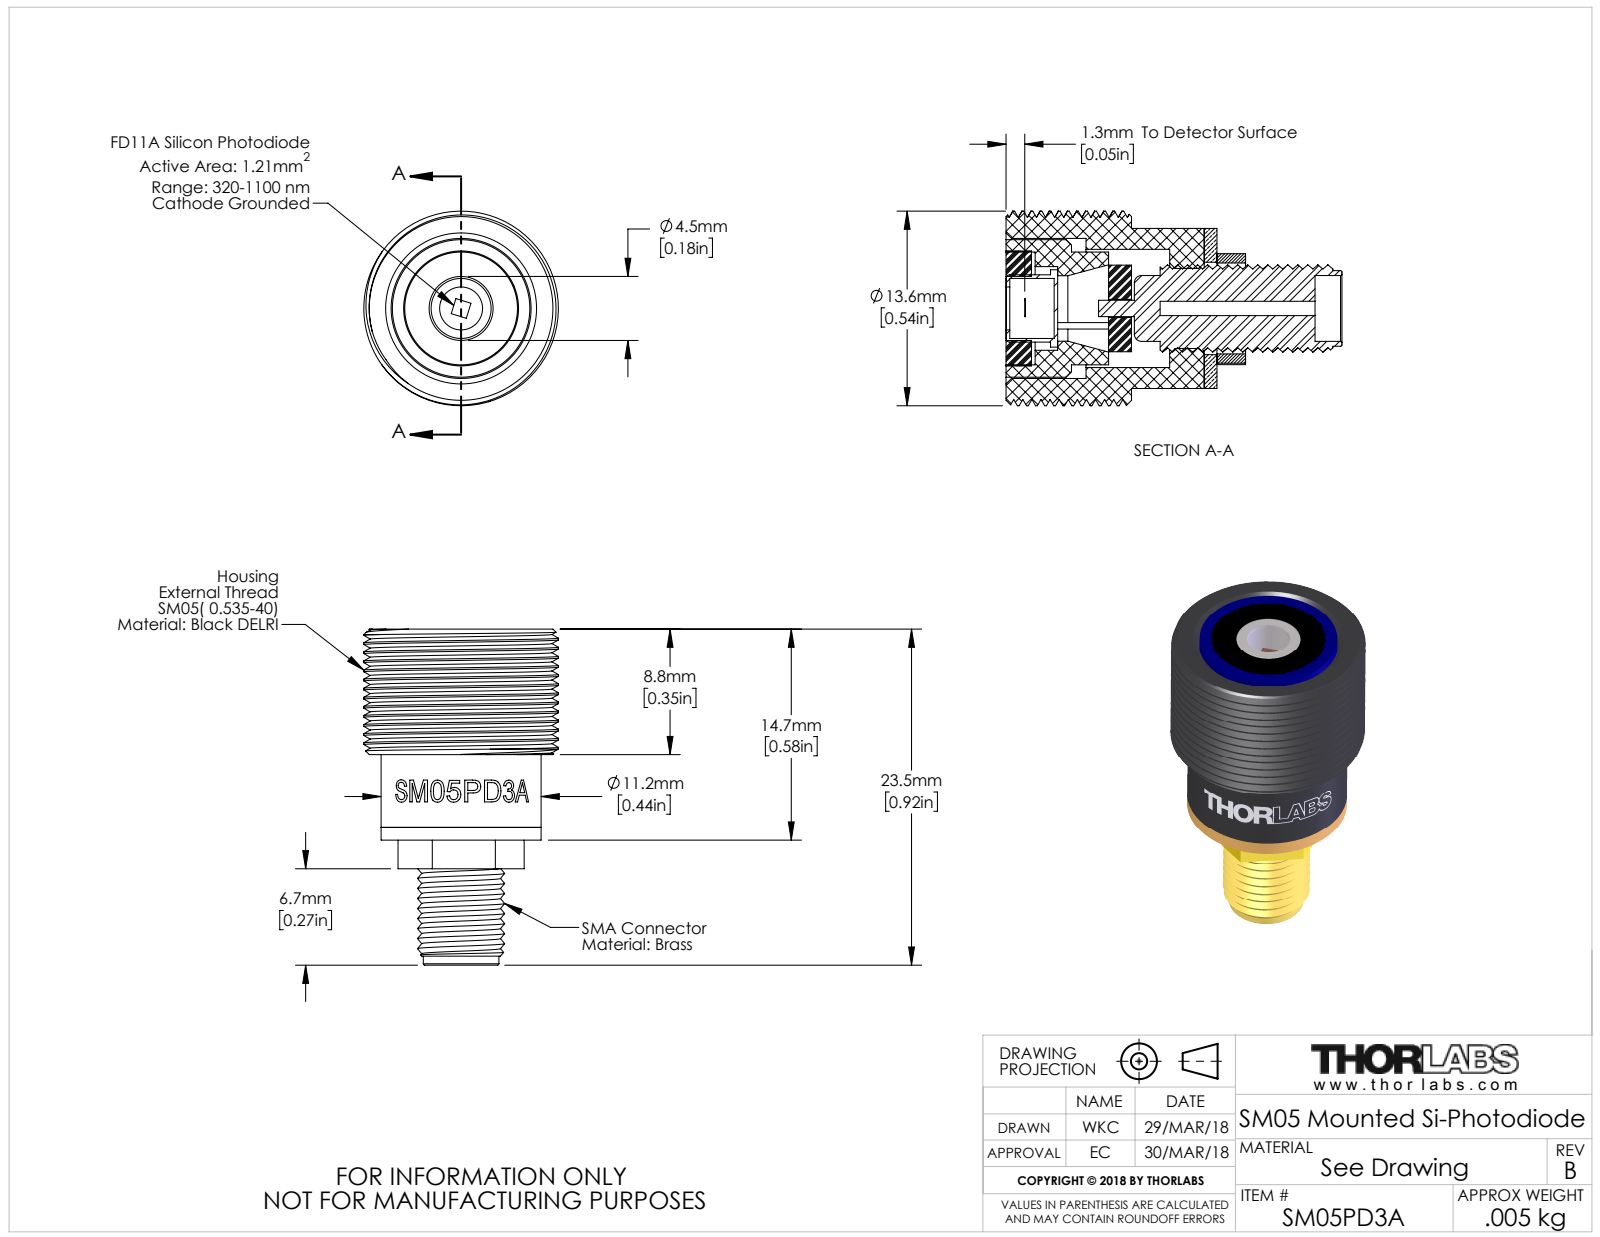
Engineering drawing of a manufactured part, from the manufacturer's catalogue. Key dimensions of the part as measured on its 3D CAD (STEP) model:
Part name (STEP PRODUCT): TTN140504-E0W
STEP written by: SolidWorks 2016 (AUTOMOTIVE_DESIGN)
Units: inches
Bodies: 8 solids, 112 faces (46 planar, 51 cylindrical, 15 other)
Overall size (bounding box): 0.924 × 0.535 × 0.535
Volume: 0.098 in³ · Surface area: 4.398 in²
Round holes (diameter × count): ⌀0.039 ×1, ⌀0.118 ×1, ⌀0.165 ×1, ⌀0.176 ×1, ⌀0.18 ×1, ⌀0.181 ×1, ⌀0.22 ×1, ⌀0.23 ×1, ⌀0.25 ×1, ⌀0.254 ×1, ⌀0.31 ×1, ⌀0.325 ×1
Round bosses / shafts (diameter × count): ⌀0.018 ×2, ⌀0.535 ×1, ⌀0.44 ×1, ⌀0.378 ×1, ⌀0.316 ×1, ⌀0.213 ×1, ⌀0.208 ×1, ⌀0.185 ×1
Main face-to-face distances: 0.545, 0.035, 0.58, 0.072, 0.14, 0.062, 0.51, 0.475, 0.07, 0.438
